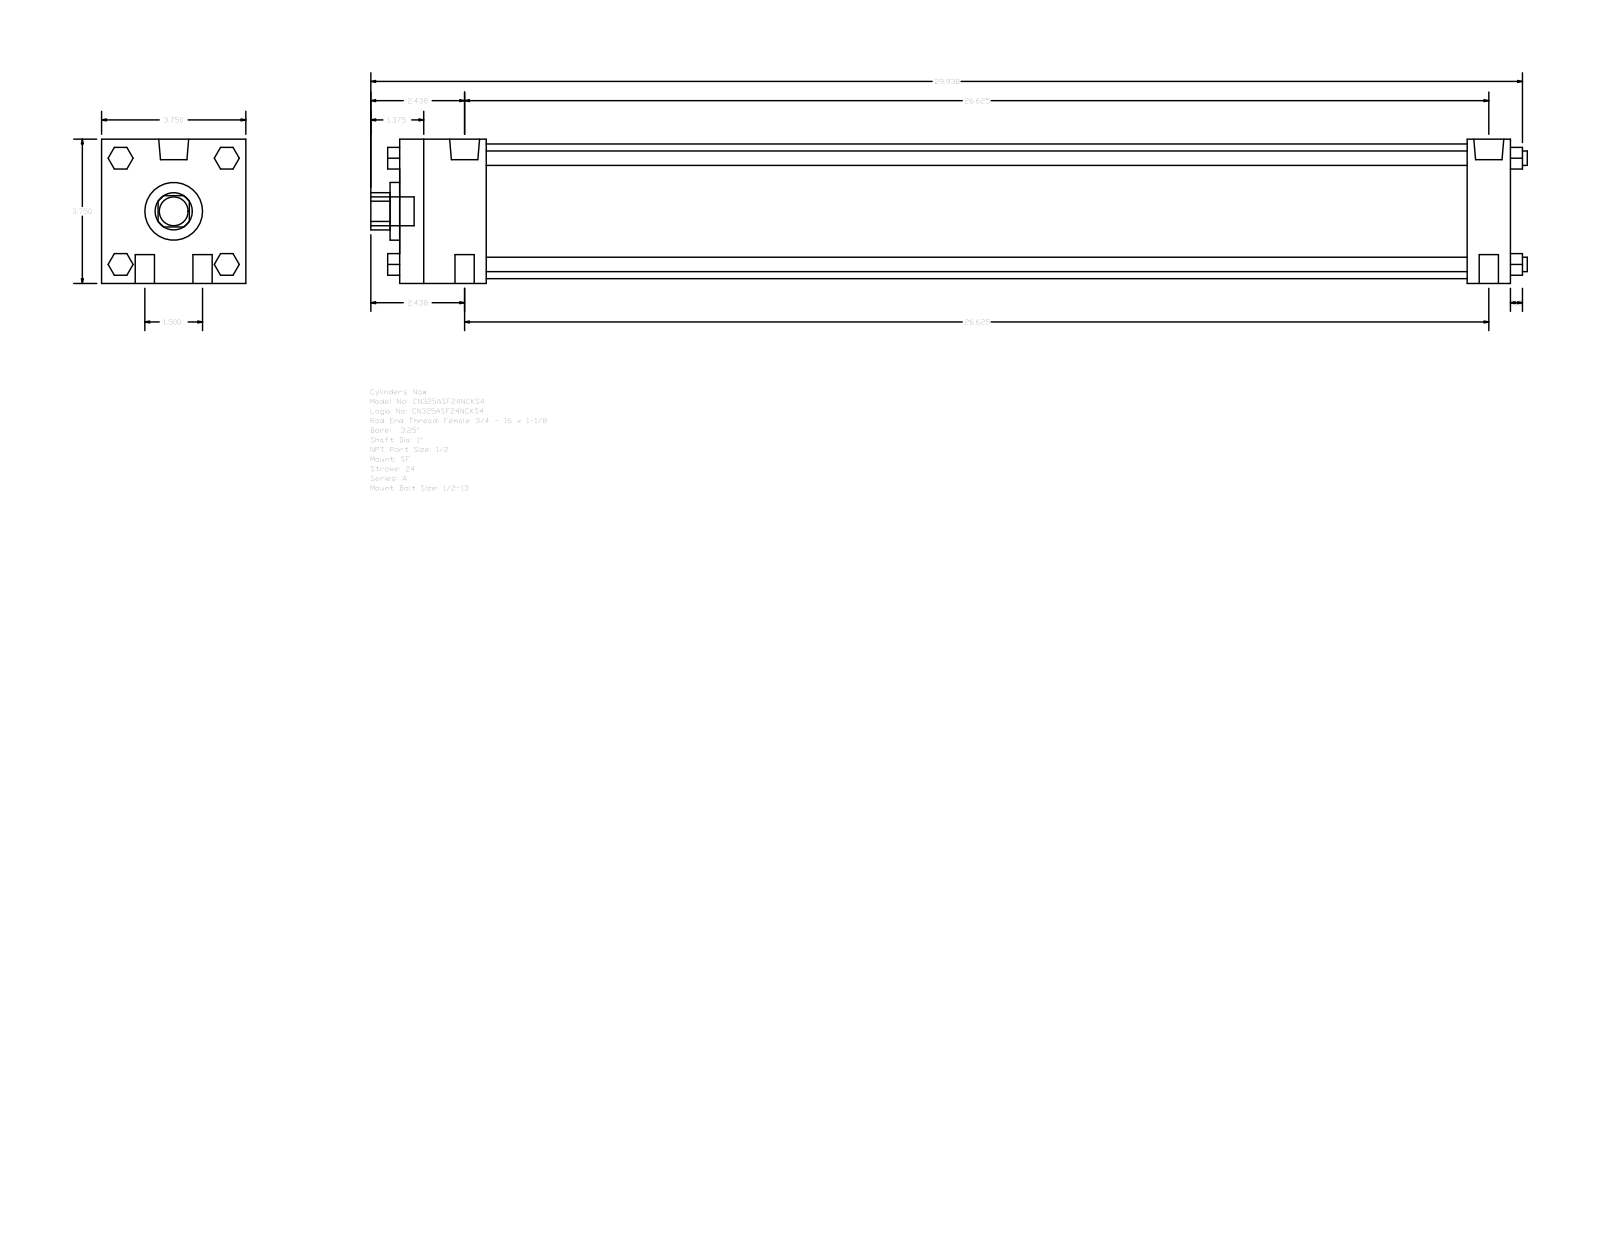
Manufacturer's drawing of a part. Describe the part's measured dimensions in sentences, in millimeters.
The part is named "A_SF__0325_1". Its 3-D file was written by "GSSL Pune (CONFIG_CONTROL_DESIGN)". It is 0 solids with 124 faces: 94 planar, 30 cylindrical and 0 other. Overall it measures 763.59 by 95.25 by 95.25 millimeters. Round holes: 1 of diameter 25.4, 1 of diameter 38.1, 1 of diameter 88.9. Round bosses or shafts: 4 of diameter 12.7, 4 of diameter 9.53, 2 of diameter 19.77, 2 of diameter 8.73, 1 of diameter 19.05. Partial cylindrical surfaces (rounded edges, fillets, slot ends): 1 of radius 12.29. The main face-to-face distances are 95.24, 733.43, 704.85, 28.58, 57.15, 647.7, 676.28, 14.28, 35.05, 60.71.
